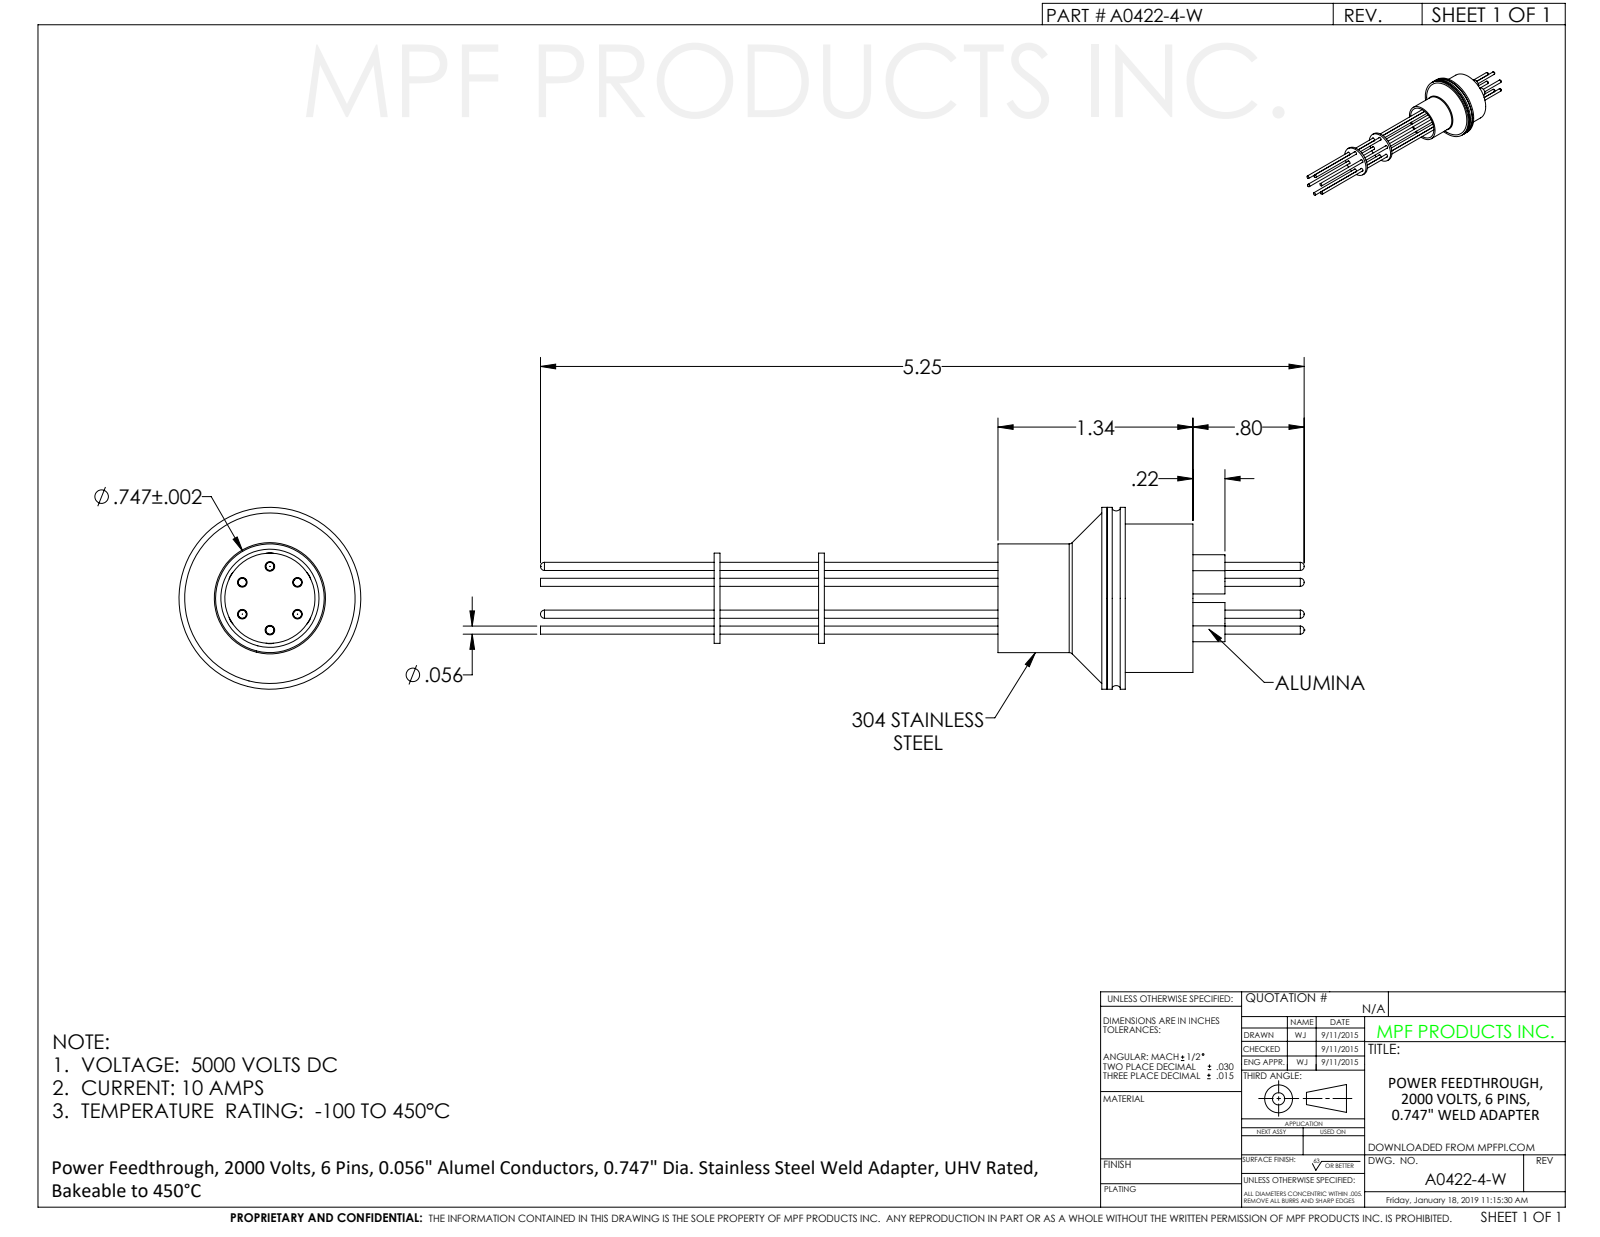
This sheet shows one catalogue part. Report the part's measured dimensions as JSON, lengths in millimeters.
{"part_name": "A0422-4-W", "step_written_by": "SolidWorks 2012 (CONFIG_CONTROL_DESIGN)", "units": "millimeters", "bodies": {"solids": 1, "faces": 209, "planar": 45, "cylindrical": 122, "other": 42}, "overall_size": [133.4, 31.8, 31.8], "volume_mm3": 6330, "surface_area_mm2": 11950, "round_holes": [[17.1, 1], [23.9, 1], [24.4, 1], [24.6, 1]], "round_bosses_or_shafts": [[4.7, 6], [4.3, 6], [1.4, 6], [31.8, 1], [25.9, 1], [24.3, 1], [19, 1], [15.7, 1]], "face_to_face_distances": [1.3, 10.9, 9.7, 1, 66.8, 69.1, 81.2, 82.2, 67.8, 79.9], "hole_center_spacings": [6.8, 4.8, 9.7, 4.7, 4.9, 6.8]}
